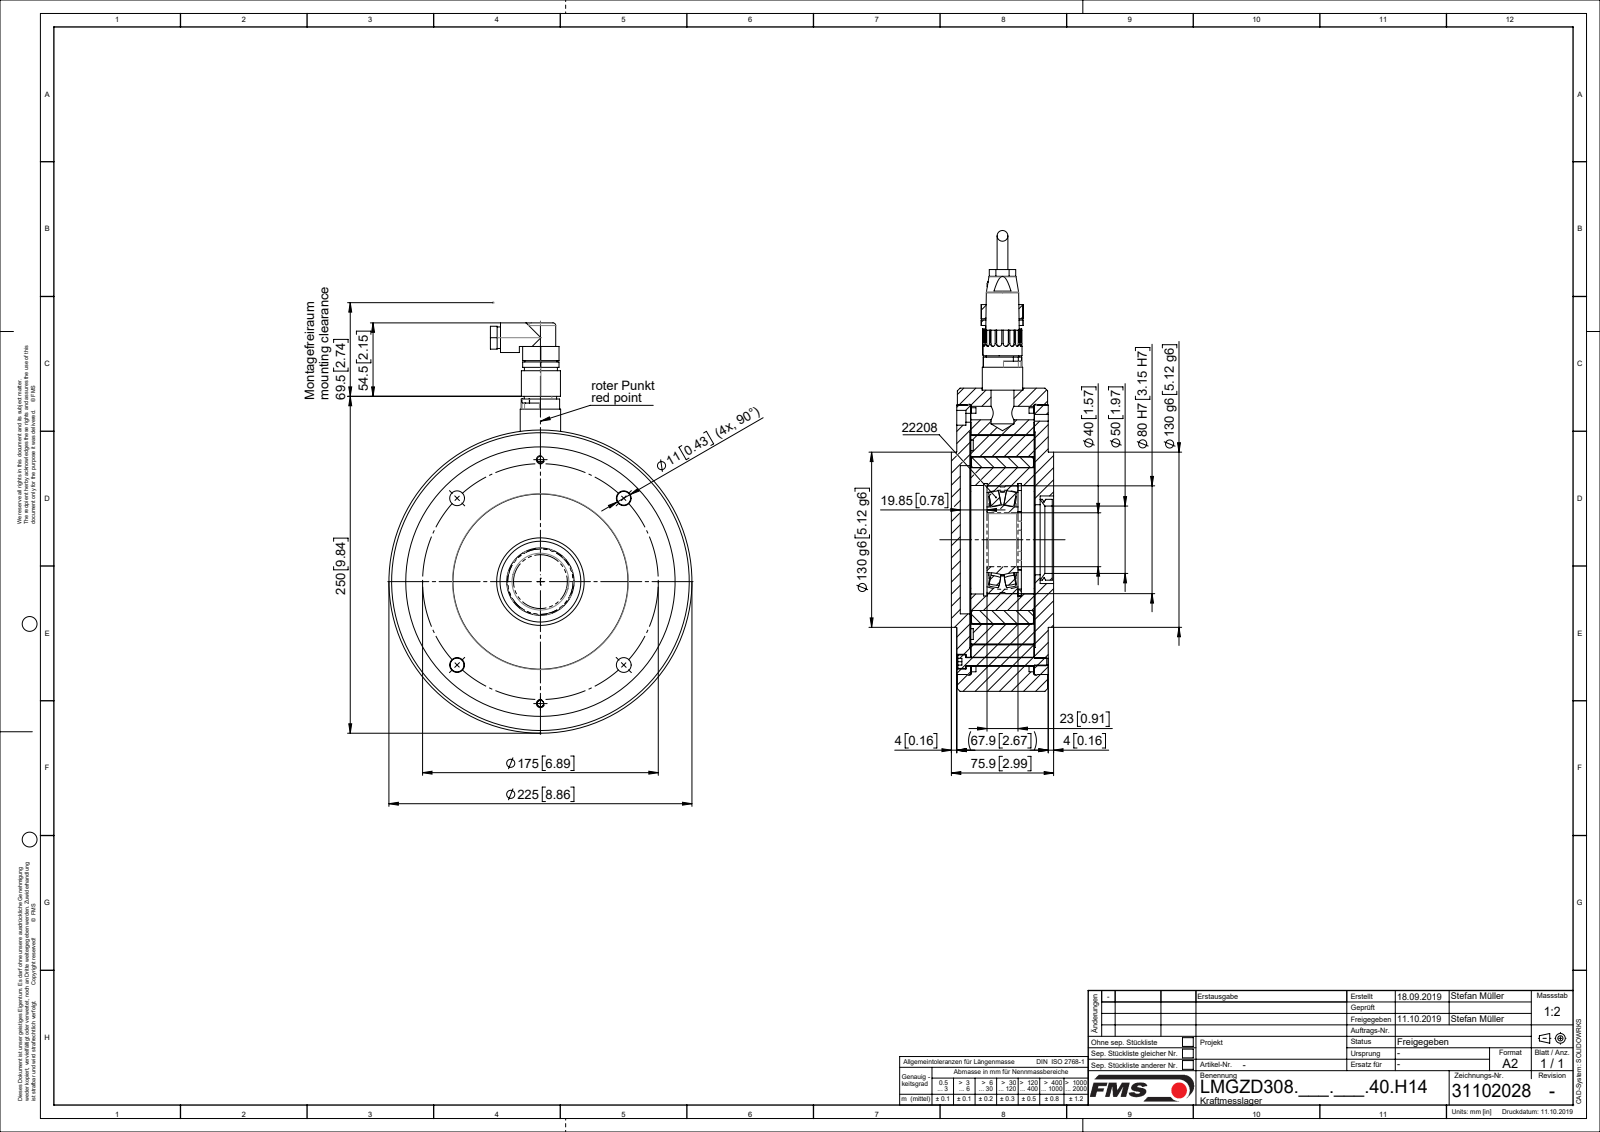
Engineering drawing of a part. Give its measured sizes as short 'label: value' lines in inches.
name: Zyl-Schr DIN912_M6x60; 49651-05_stp_01; 49027_01; 31101677_V-050A (+8 more)
written by: SolidWorks 2018 (CONFIG_CONTROL_DESIGN)
unit: in
bodies: 48 solids, 803 faces (227 planar, 312 cylindrical, 264 other)
size: 11.988 × 8.858 × 2.988
volume: 148.2 in³; area: 709.2 in²
holes: 6× ⌀0.433, 4× ⌀0.098, 3× ⌀0.126, 2× ⌀0.118, 2× ⌀0.134, 2× ⌀0.142, 2× ⌀0.197, 2× ⌀0.26, 2× ⌀0.394, 2× ⌀0.402, 1× ⌀0.315, 1× ⌀0.551
bosses: 13× ⌀0.085, 2× ⌀0.945, 2× ⌀0.866, 2× ⌀0.217, 2× ⌀0.118, 1× ⌀8.858, 1× ⌀7.835, 1× ⌀7.402
rounds: 4× R0.004, 4× R0.433, 2× R0.079, 2× R0.118, 2× R0.193, 1× R1.309, 1× R3.11, 1× R3.228
face distances: 1.86, 0.402, 0.411, 2.262, 2.272, 1.89, 0.02, 0.03, 1.88, 0.382
hole spacings: 0.64, 0.885, 0.906, 2.442, 2.684, 3.445, 4.872, 5.293
